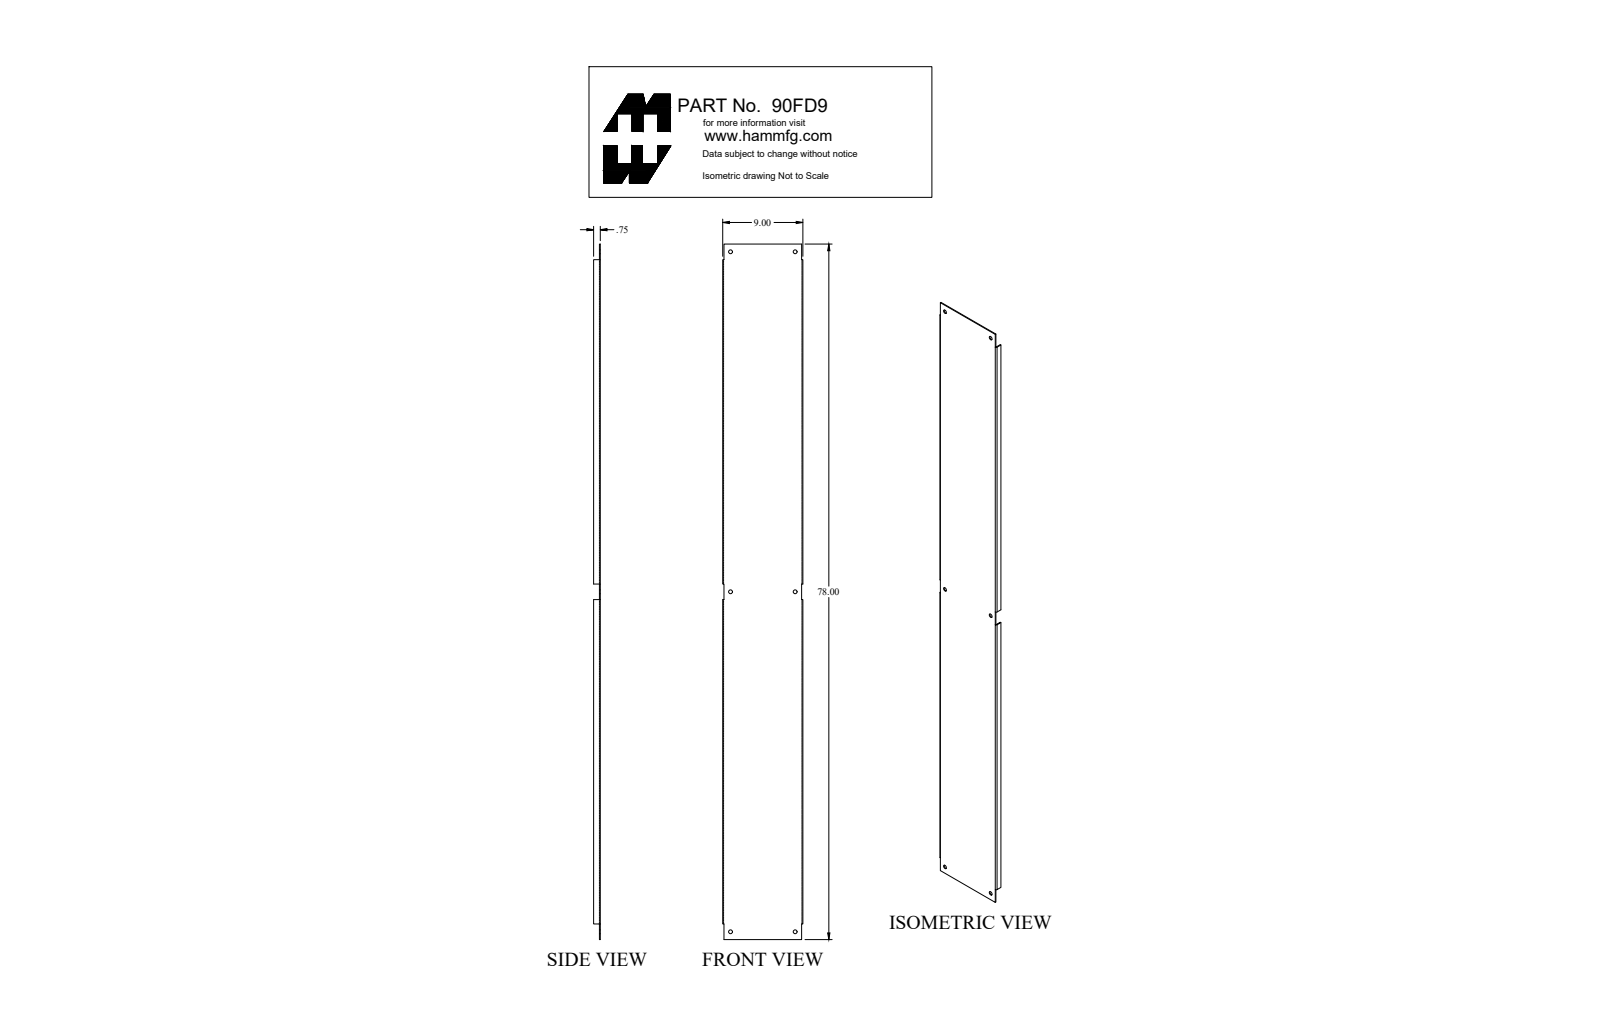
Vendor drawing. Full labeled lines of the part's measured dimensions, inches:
Part name (STEP PRODUCT): 90FD9_Default
STEP written by: SolidWorks 2018 (CONFIG_CONTROL_DESIGN)
Units: inches
Bodies: 1 solid, 50 faces (30 planar, 20 cylindrical, 0 other)
Overall size (bounding box): 78 × 9 × 0.75
Volume: 74.95 in³ · Surface area: 1 596 in²
Round holes (diameter × count): ⌀0.437 ×6
Partial cylindrical surfaces — rounded edges, fillets, slot ends (radius × count): R0.048 ×2, R0.143 ×2
Main face-to-face distances: 0.095, 8.905, 8.81, 9, 0.75, 0.655, 0.143, 8.857, 0.048, 8.762
Hole centre spacings: 38.125, 38.809, 7.25, 76.25, 76.594
